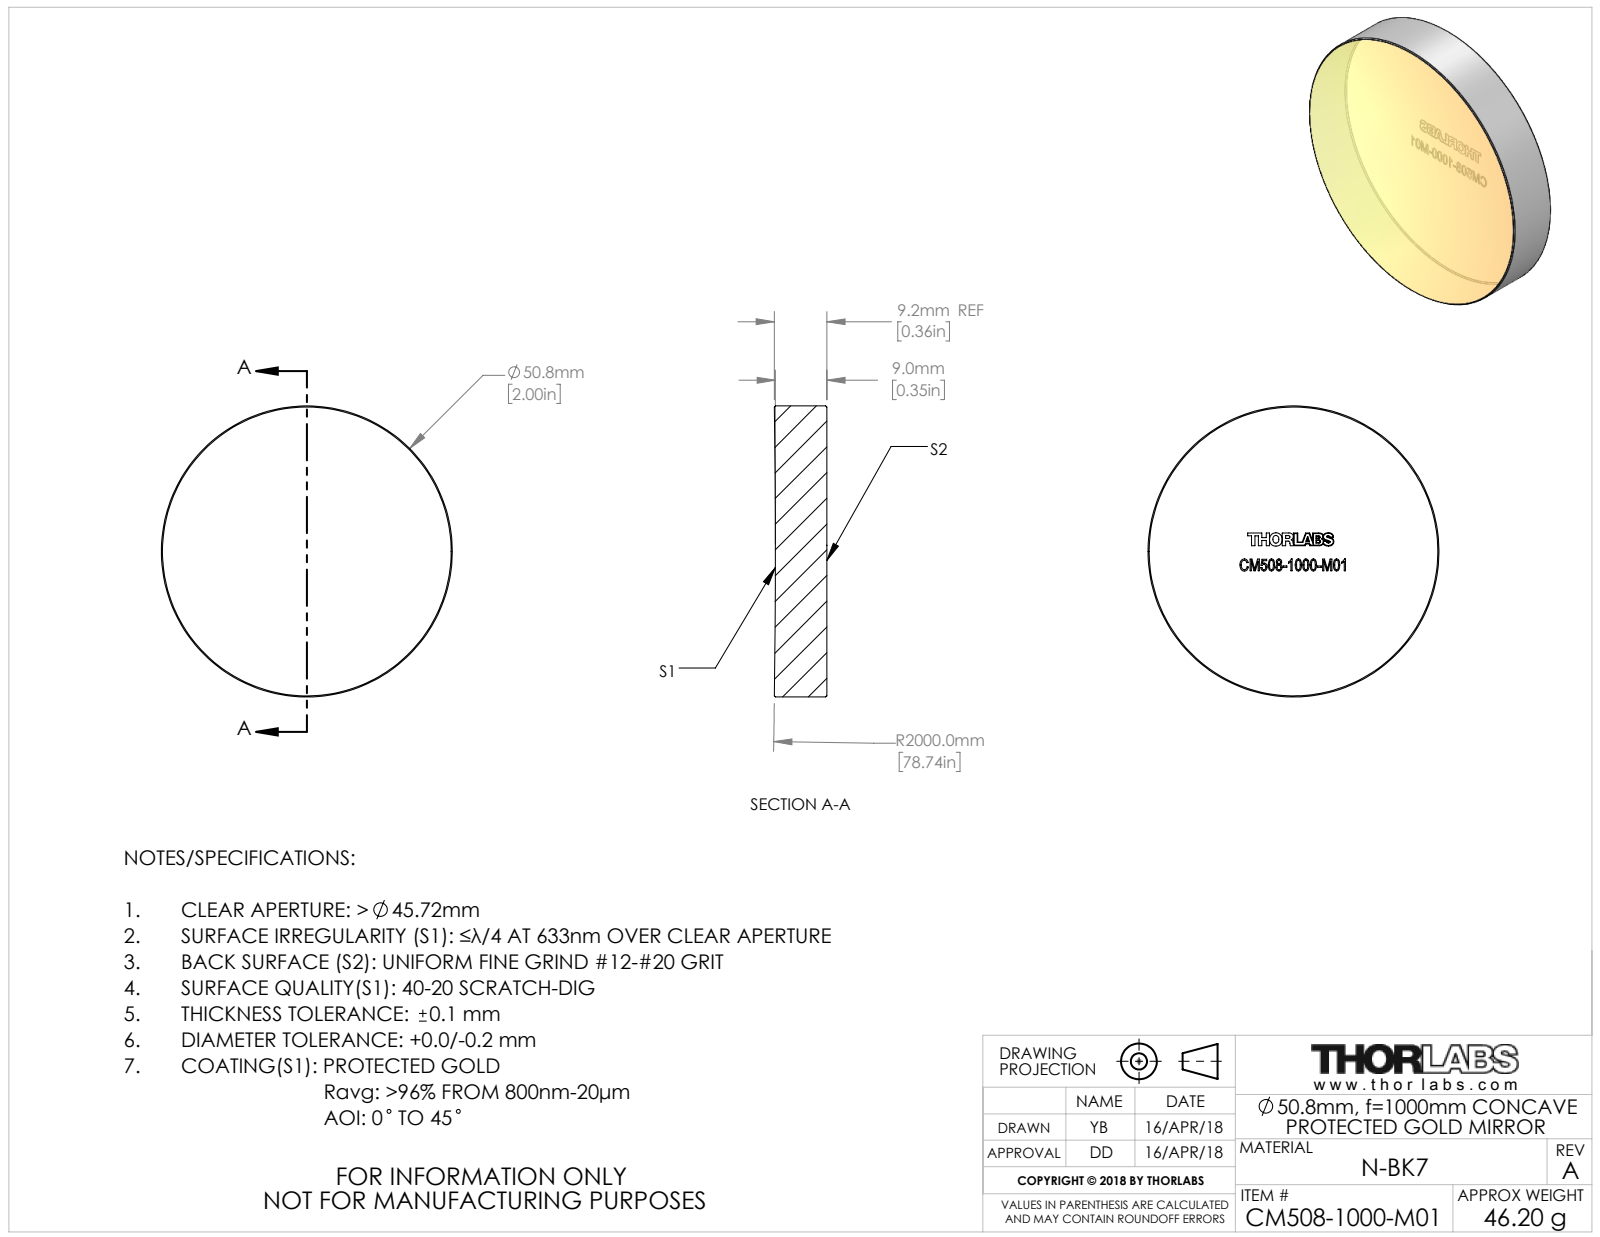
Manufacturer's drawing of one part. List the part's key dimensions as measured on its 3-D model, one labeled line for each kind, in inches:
Part name (STEP PRODUCT): TTN153338-E0W
STEP written by: SolidWorks 2018 (CONFIG_CONTROL_DESIGN)
Units: inches
Bodies: 1 solid, 45 faces (37 planar, 2 cylindrical, 6 other)
Overall size (bounding box): 2 × 2 × 0.361
Volume: 1.123 in³ · Surface area: 8.491 in²
Round bosses / shafts (diameter × count): ⌀2 ×1
